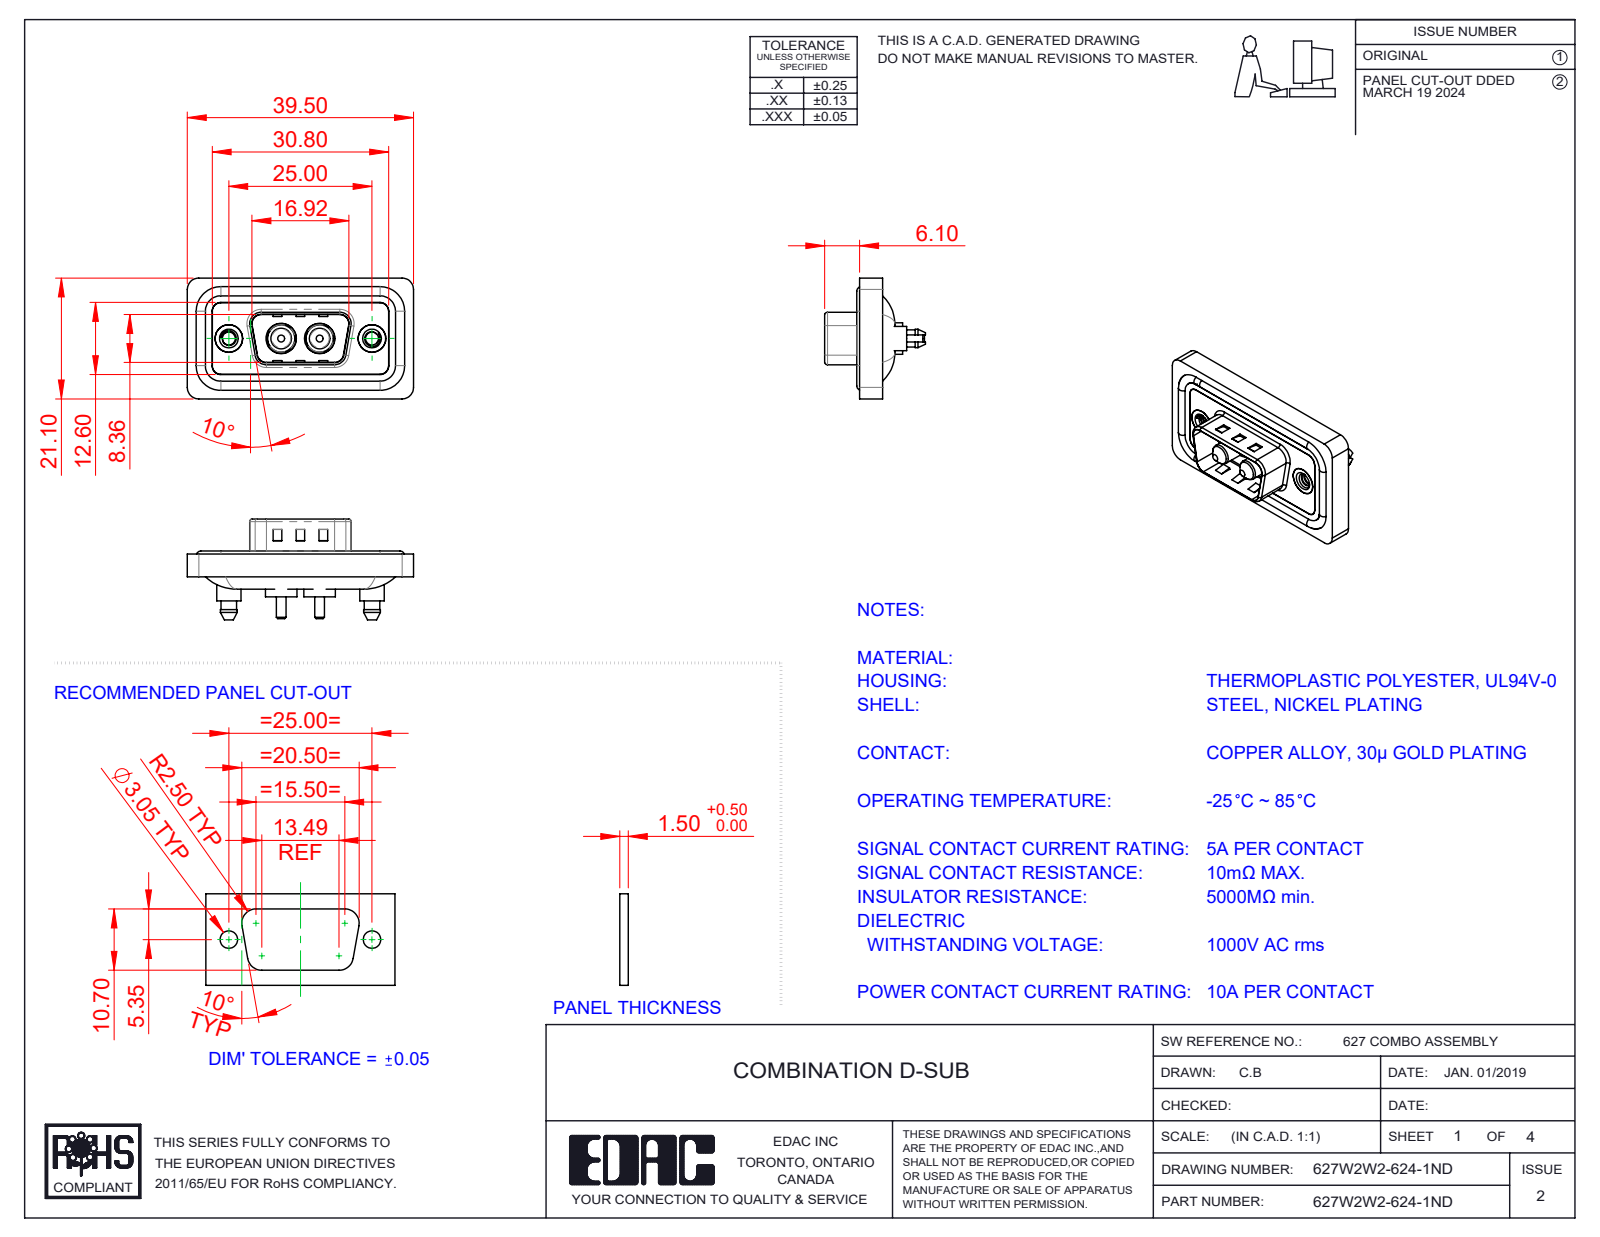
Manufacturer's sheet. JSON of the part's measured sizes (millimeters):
{"part_name": "627Combo Housing_2W2; 627Combo Waterproof Housing_09 Contacts; 627Combo Threaded Boardlock_D; 627Combo Threaded Boardlock_5 (+4 more)", "step_written_by": "SolidWorks 2023 (CONFIG_CONTROL_DESIGN)", "units": "millimeters", "bodies": {"solids": 11, "faces": 547, "planar": 181, "cylindrical": 258, "other": 108}, "overall_size": [39.5, 21.1, 17.6], "volume_mm3": 4566, "surface_area_mm2": 7295, "round_holes": [[2.26, 2], [4, 2], [4.8, 2], [4.85, 2], [5, 2], [5.3, 2]], "round_bosses_or_shafts": [[1.6, 4], [5.5, 2], [5.4, 2], [5.2, 2], [4.9, 2], [4.75, 2], [4.25, 2], [3.75, 2]], "partial_cylinders_radius": [[1.5, 24], [2, 18], [1.6, 10], [0.5, 8], [0.25, 4], [0.6, 4], [0.65, 4], [0.9, 4]], "face_to_face_distances": [0.4, 1.1, 2.9, 1.5, 3.1, 0.5, 1.6, 4, 0.7, 2.5], "hole_center_spacings": [9.14, 15.86, 6.72, 25]}
